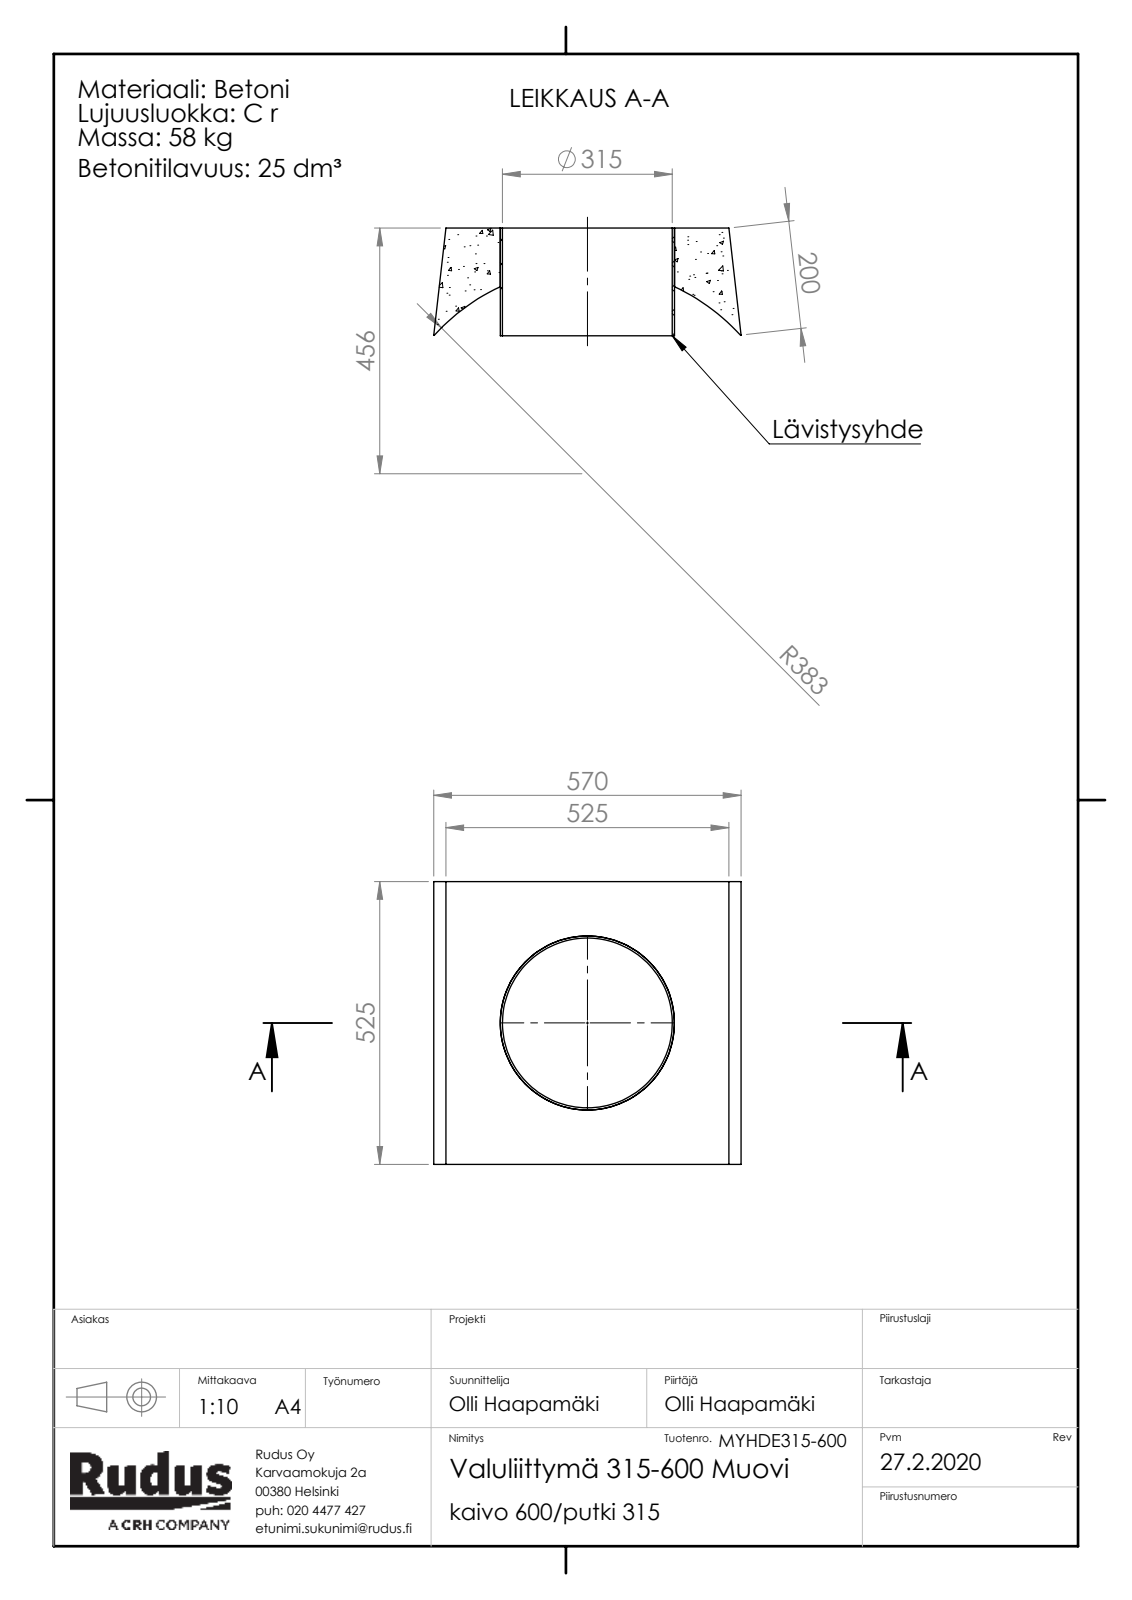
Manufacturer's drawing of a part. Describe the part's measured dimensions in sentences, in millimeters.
The part is named "muovi-lavistysyhde; Rudus MYHDE315-600 Valuliittymä 315-600 Muovi; kaivo-osa-valuliittyma-runko_muovi". Its 3-D file was written by "SolidWorks 2019 (CONFIG_CONTROL_DESIGN)". It is 2 solids with 16 faces: 9 planar, 7 cylindrical and 0 other. Overall it measures 570 by 525 by 200 millimeters. Its volume is 25 320 000 cubic millimeters and its surface area 1 277 000 square millimeters. Round holes: 1 of diameter 315, 1 of diameter 323. Partial cylindrical surfaces (rounded edges, fillets, slot ends): 1 of radius 383. The main face-to-face distances are 525, 200.
